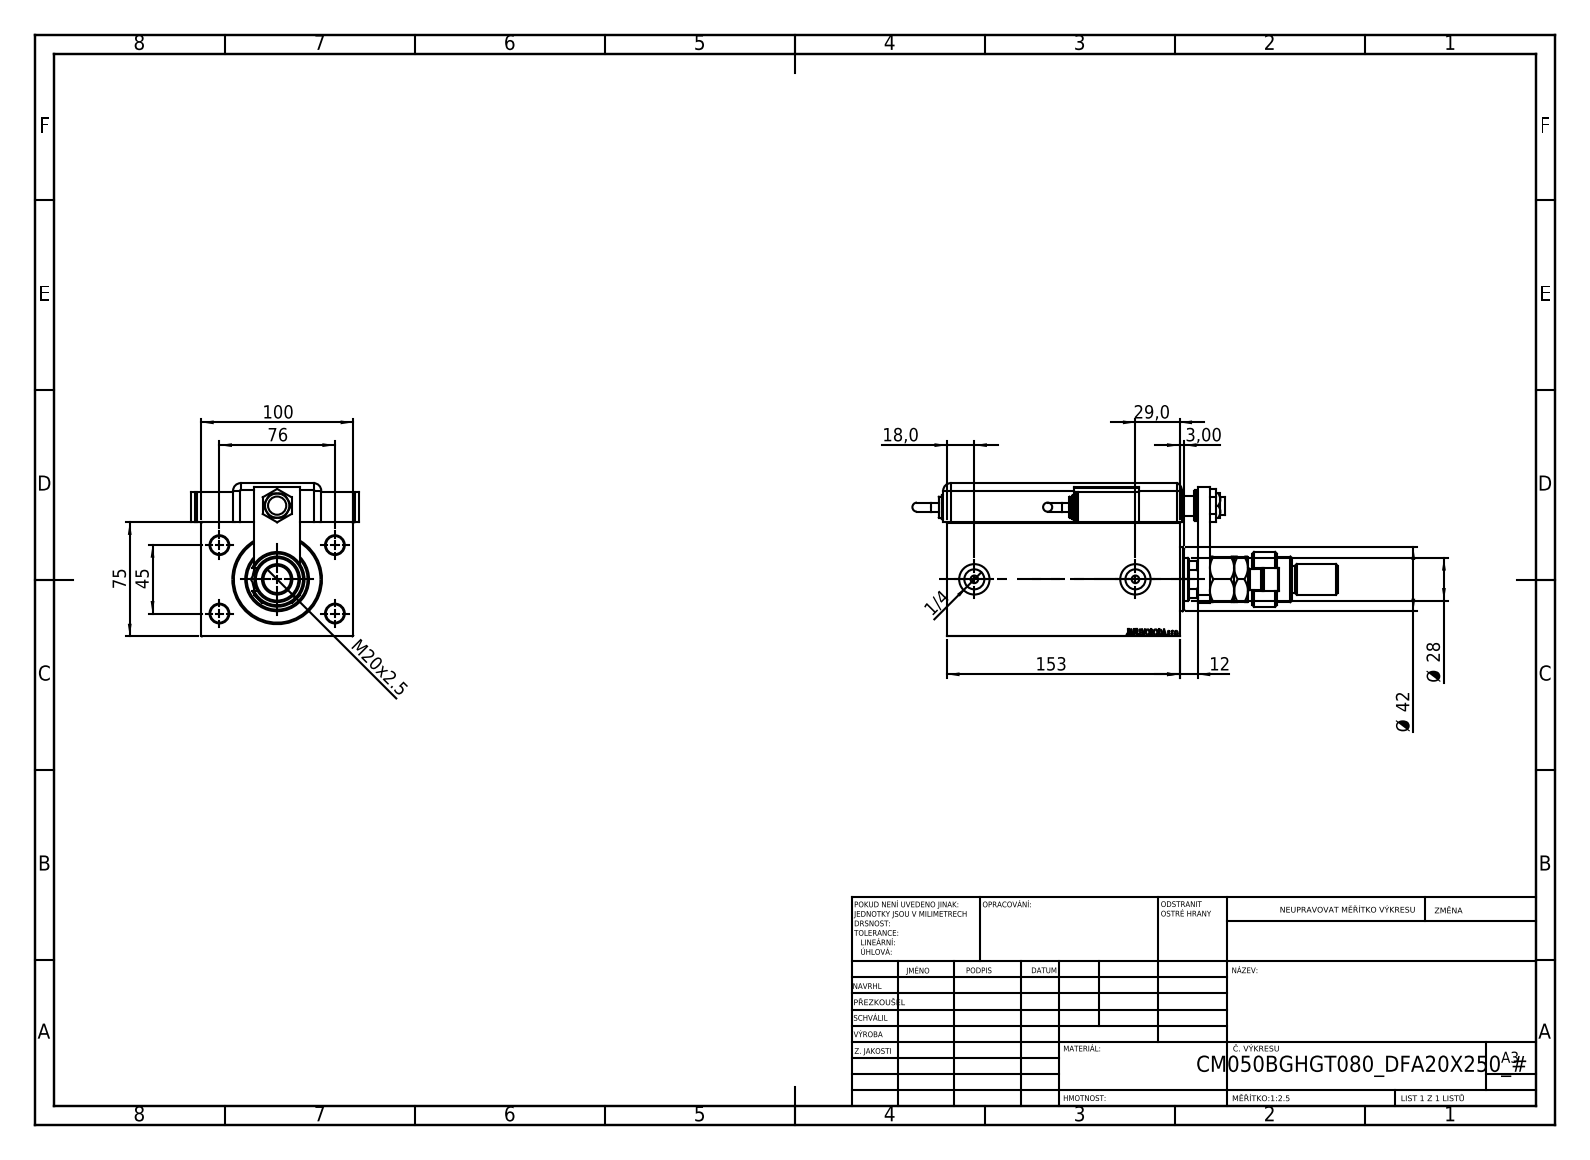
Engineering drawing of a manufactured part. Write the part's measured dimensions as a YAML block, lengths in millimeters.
part_name: "V450CM_VC_B; V450CM_B_VCP; MFA; TYC (+7 more)"
step_written_by: "SolidWorks 2019 (CONFIG_CONTROL_DESIGN)"
units: millimeters
bodies: {solids: 15, faces: 1353, planar: 636, cylindrical: 124, other: 593}
overall_size: [279.76, 111, 100.8]
volume: 1234000
surface_area: 208492
round_holes:
  - {diameter: 12, count: 5}
  - {diameter: 20, count: 3}
  - {diameter: 4, count: 2}
  - {diameter: 5, count: 2}
  - {diameter: 8, count: 2}
  - {diameter: 13.16, count: 2}
  - {diameter: 13, count: 1}
  - {diameter: 14, count: 1}
  - {diameter: 18.5, count: 1}
  - {diameter: 28, count: 1}
  - {diameter: 31.5, count: 1}
  - {diameter: 32.5, count: 1}
round_bosses_or_shafts:
  - {diameter: 20, count: 3}
  - {diameter: 14, count: 3}
  - {diameter: 16, count: 2}
  - {diameter: 6, count: 2}
  - {diameter: 42, count: 1}
  - {diameter: 36, count: 1}
  - {diameter: 30, count: 1}
  - {diameter: 22, count: 1}
partial_cylinders:
  - {radius: 5, count: 9}
  - {radius: 7.5, count: 1}
  - {radius: 10, count: 1}
  - {radius: 12, count: 1}
  - {radius: 13.5, count: 1}
face_to_face_distances: [75, 3, 100, 100.8, 25.8, 20, 24, 14, 153, 97.8]
hole_center_spacings: [44.16, 45, 46.04, 76, 80.53, 88.32, 20, 48.5]
